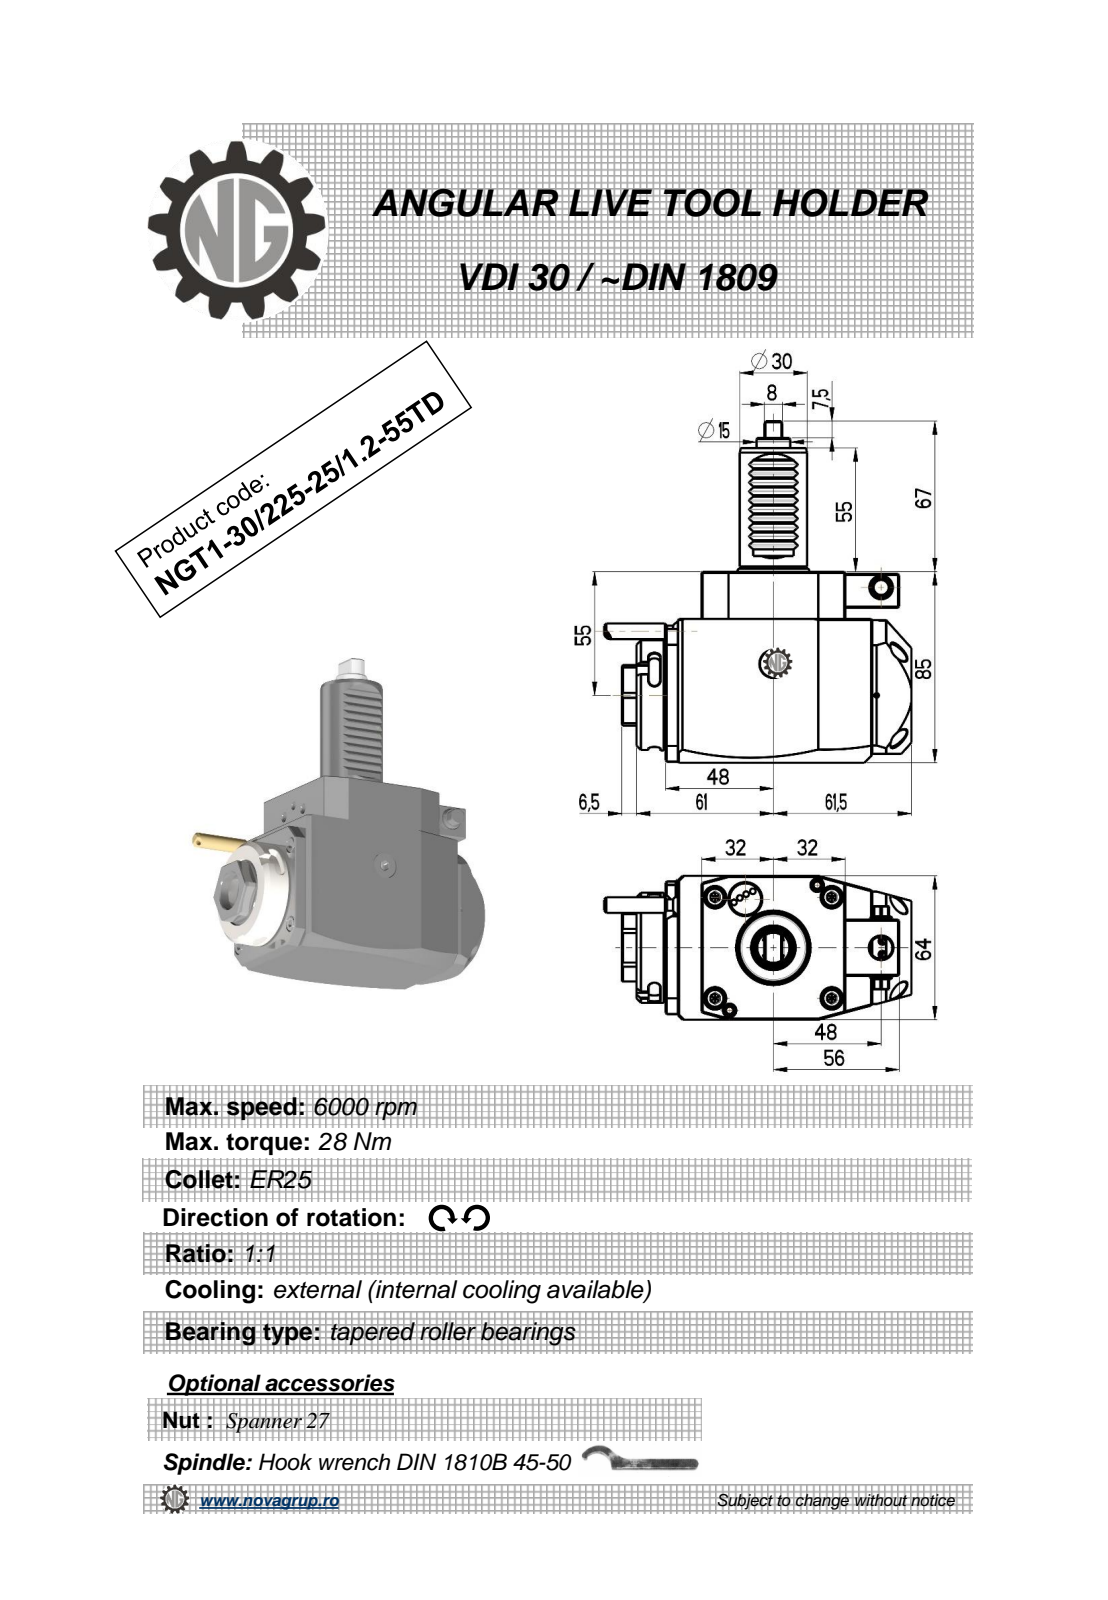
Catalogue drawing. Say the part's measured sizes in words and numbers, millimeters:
The part is named "NGT1_30_225_25_1_2_55TD". Its 3-D file was written by "PRO/ENGINEER BY PARAMETRIC TECHNOLOGY CORPORATION, 2010280 (CONFIG_CONTROL_DESIGN)". It is 1 solid with 352 faces: 192 planar, 88 cylindrical and 72 other. Overall it measures 152 by 136.88 by 64 millimeters. Its volume is 557 633 cubic millimeters and its surface area 50 808 square millimeters. Round holes: 1 of diameter 2.5, 1 of diameter 3, 1 of diameter 9.5, 1 of diameter 10, 1 of diameter 18. Round bosses or shafts: 2 of diameter 8, 1 of diameter 49, 1 of diameter 42, 1 of diameter 30, 1 of diameter 15, 1 of diameter 10, 1 of diameter 7, 1 of diameter 5. Partial cylindrical surfaces (rounded edges, fillets, slot ends): 10 of radius 0.3, 6 of radius 2.5, 2 of radius 0.8, 2 of radius 180, 1 of radius 3.85, 1 of radius 4.25, 1 of radius 4.5, 1 of radius 7.2. The main face-to-face distances are 64, 85, 16, 109.5, 13, 21, 80, 122.5, 29, 93.5. The hole center spacings are 26.17, 34.25, 46.5.
